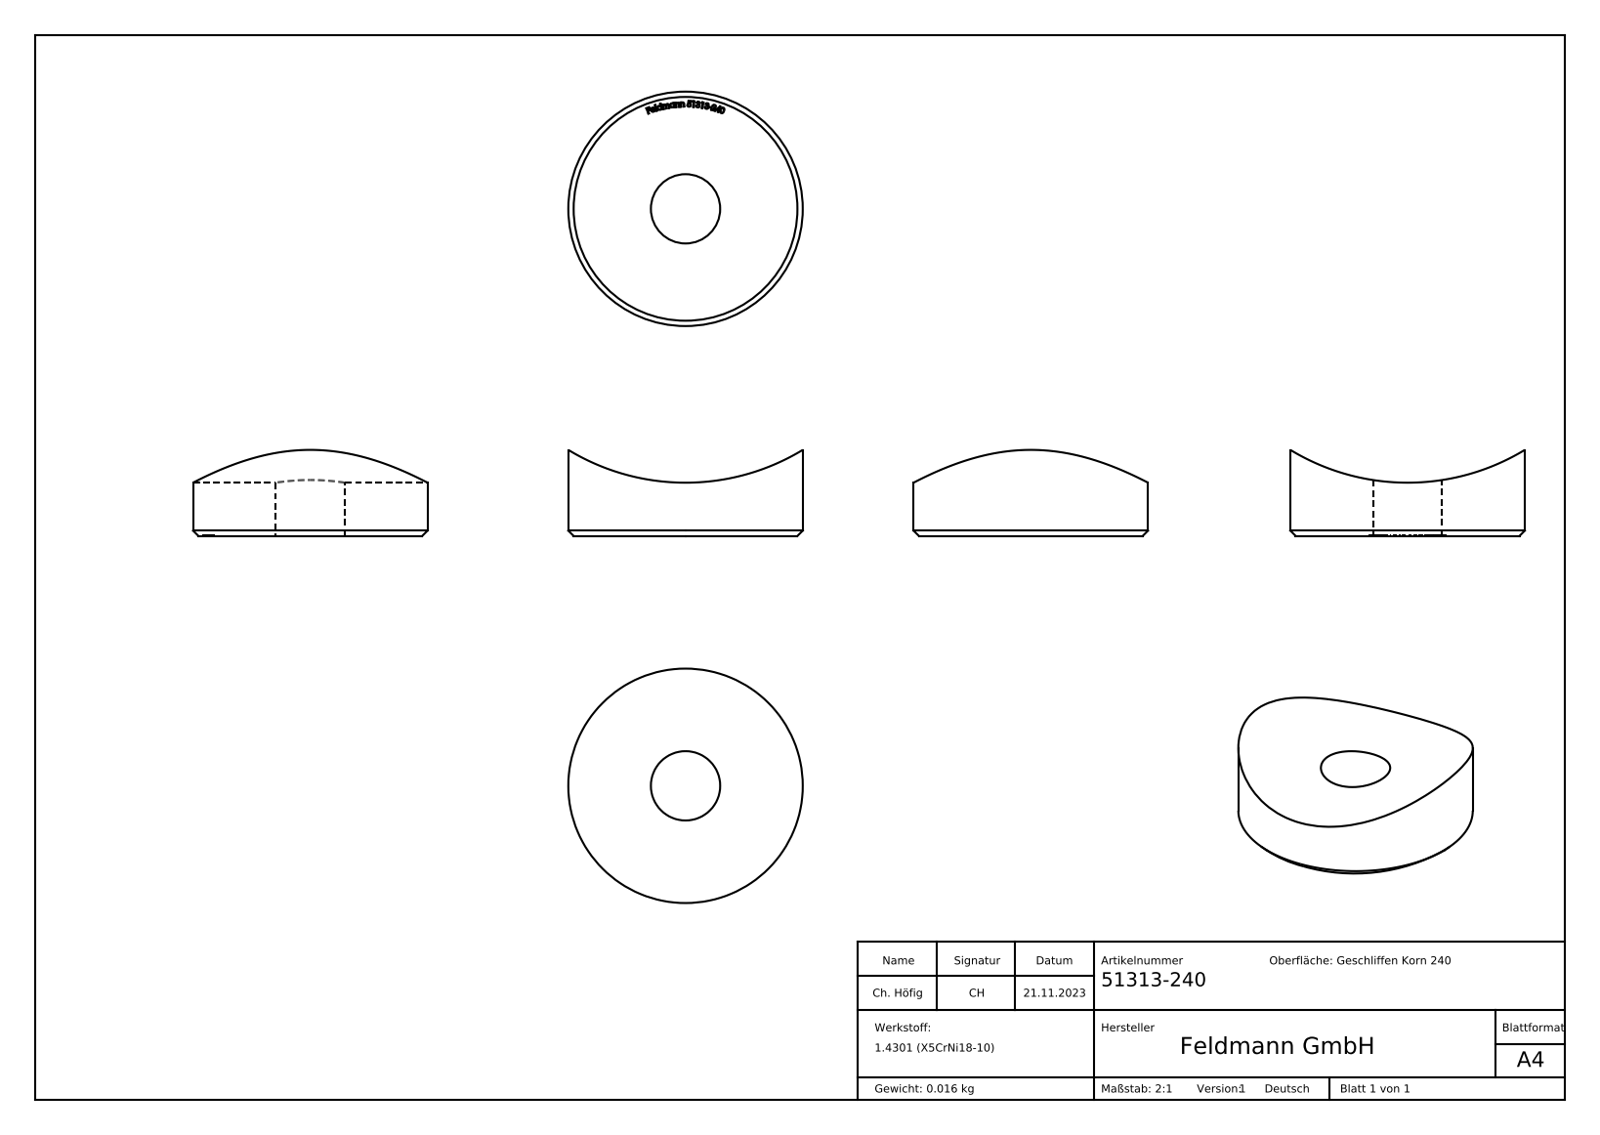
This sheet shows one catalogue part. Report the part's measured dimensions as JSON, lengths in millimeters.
{"part_name": "51313-240", "step_written_by": "SolidWorks 2018 (CONFIG_CONTROL_DESIGN)", "units": "millimeters", "bodies": {"solids": 1, "faces": 227, "planar": 124, "cylindrical": 3, "other": 100}, "overall_size": [22, 22, 8.08], "volume_mm3": 2006, "surface_area_mm2": 1246, "round_holes": [[6.5, 1]], "round_bosses_or_shafts": [[22, 1]], "partial_cylinders_radius": [[21.2, 1]], "face_to_face_distances": [0.32, 0.54, 0.59, 0.53, 0.39, 0.48, 0.35, 0.4, 0.36, 0.31]}
